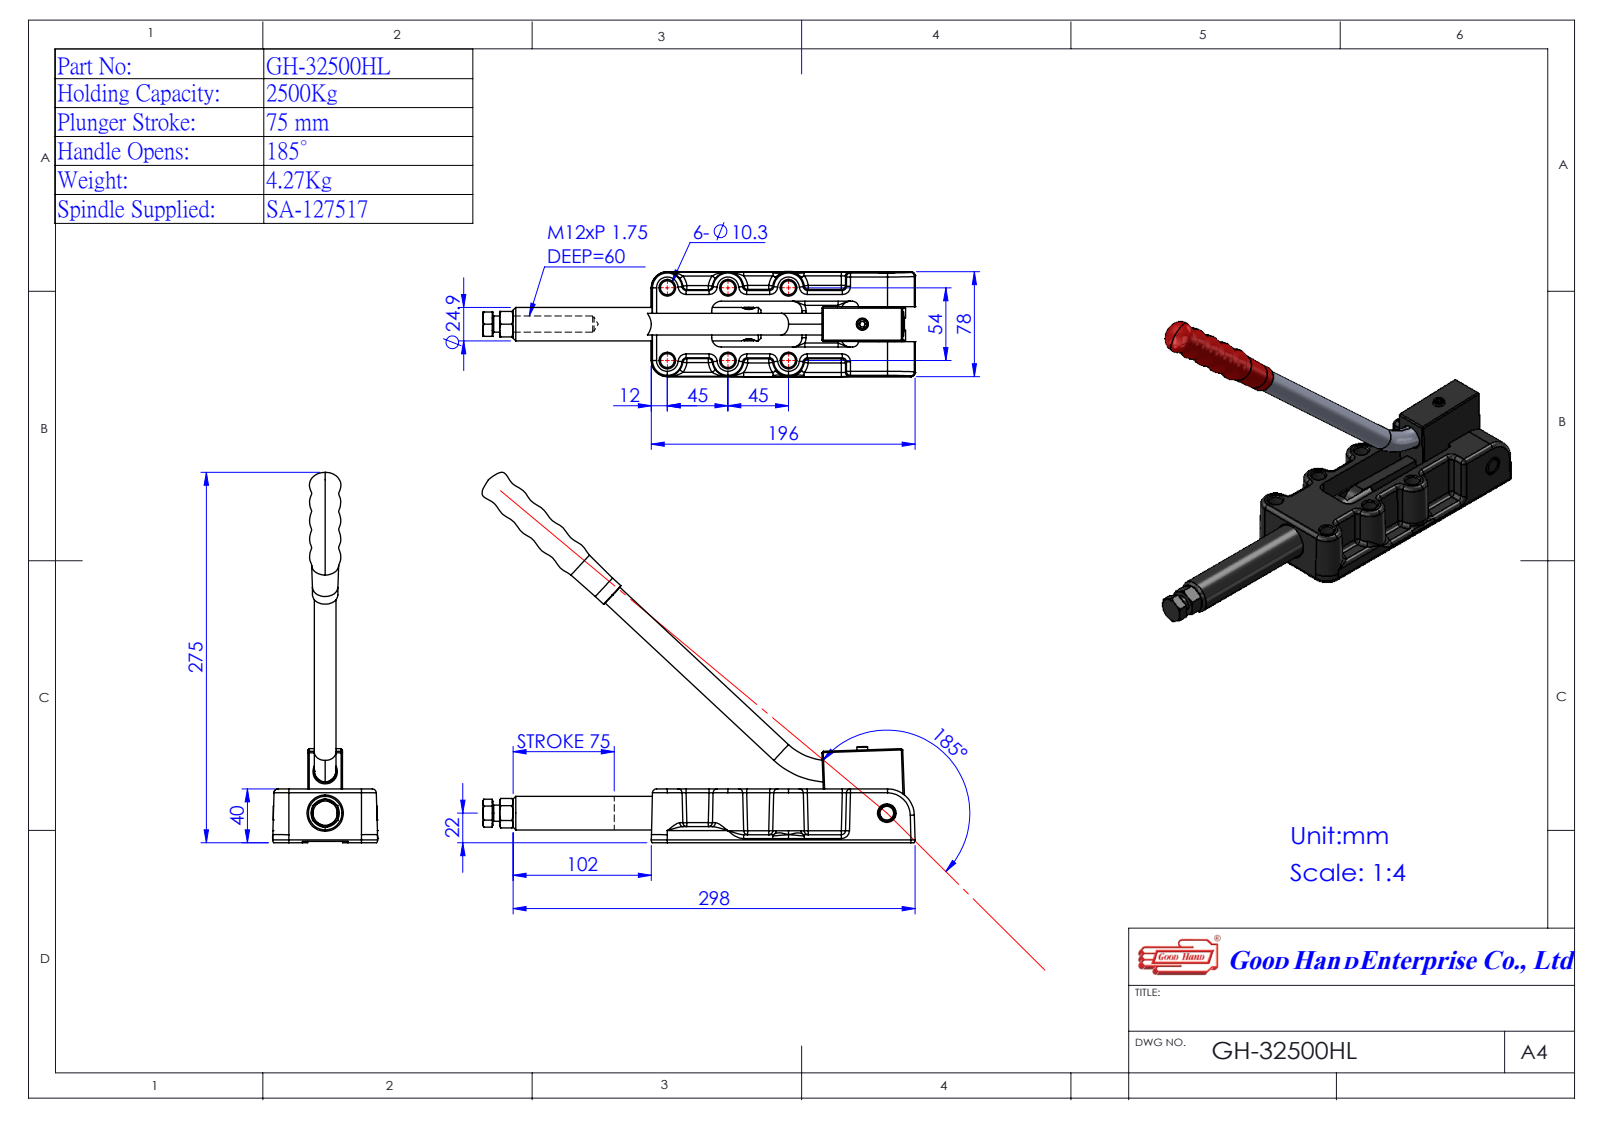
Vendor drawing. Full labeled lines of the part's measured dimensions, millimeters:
Part name (STEP PRODUCT): GH-32500HL(簡化)-1; Group1^GH-32500HL(簡化); 13250005-1^GH-32500HL(簡化)-1; Group5^GH-32500HL(簡化)-1 (+2 more)
STEP written by: SolidWorks 2016 (AUTOMOTIVE_DESIGN)
Units: millimetres
Bodies: 5 solids, 350 faces (105 planar, 102 cylindrical, 143 other)
Overall size (bounding box): 319.91 × 268.18 × 78.21
Volume: 563 978 mm³ · Surface area: 129 351 mm²
Round holes (diameter × count): ⌀10.3 ×6, ⌀7 ×2, ⌀10 ×1, ⌀10.25 ×1, ⌀24.9 ×1
Round bosses / shafts (diameter × count): ⌀18.8 ×1, ⌀18 ×1, ⌀16 ×1, ⌀12 ×1, ⌀7 ×1
Partial cylindrical surfaces — rounded edges, fillets, slot ends (radius × count): R3 ×29, R7 ×6, R4.5 ×2, R12.5 ×2, R20 ×1
Main face-to-face distances: 8.4, 17.5, 4.1, 29.9, 34, 40, 12.5, 21.5, 17.4, 9.1
Hole centre spacings: 45, 70.29, 54, 90, 104.96, 38, 64.5, 102.47
